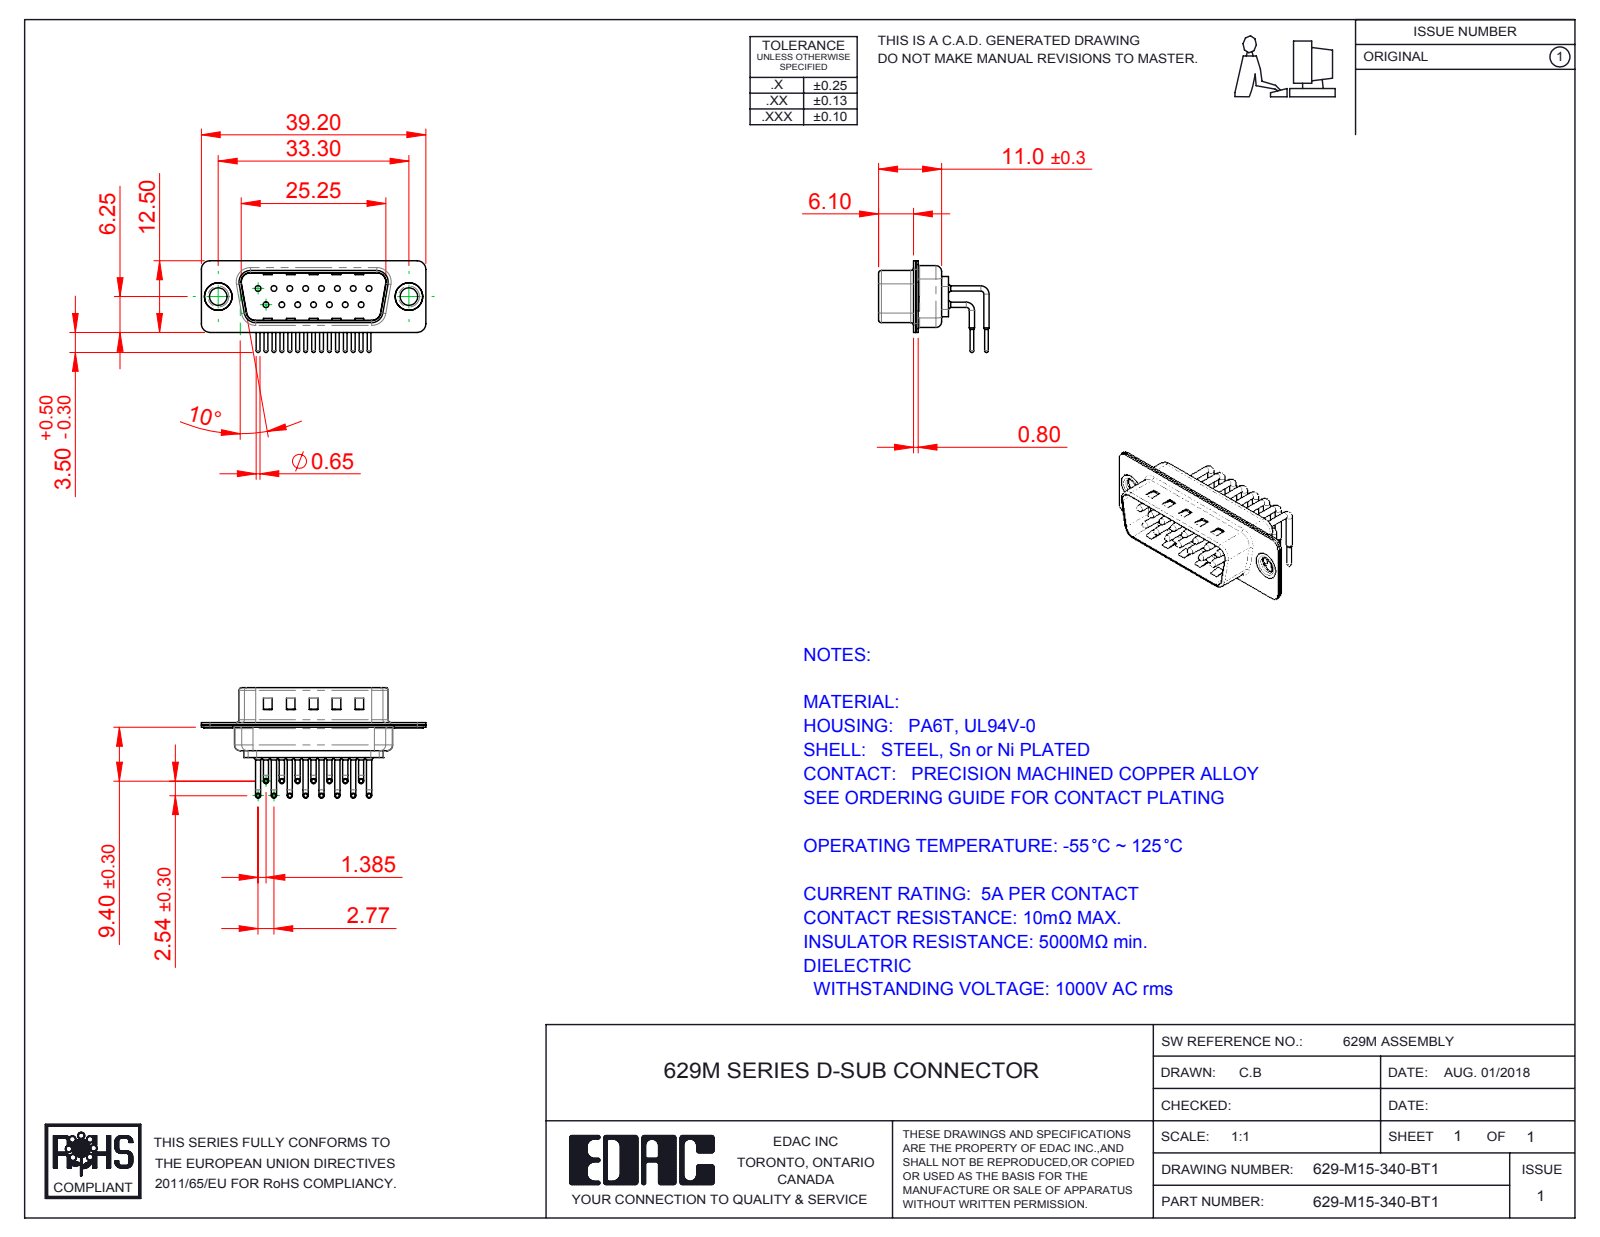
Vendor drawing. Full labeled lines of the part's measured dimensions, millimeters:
Part name (STEP PRODUCT): 629M Thru Hole Rivet; 629M Contact Row 1; 629M Contact Row 2; 629-M15-340-BT1 (+3 more)
STEP written by: SolidWorks 2016 (CONFIG_CONTROL_DESIGN)
Units: millimetres
Bodies: 20 solids, 1964 faces (1099 planar, 657 cylindrical, 208 other)
Overall size (bounding box): 39.2 × 19.29 × 16
Volume: 1 881 mm³ · Surface area: 5 213 mm²
Round holes (diameter × count): ⌀1 ×15, ⌀1.7 ×15, ⌀2 ×15, ⌀3.05 ×2, ⌀4 ×2, ⌀4.8 ×2
Round bosses / shafts (diameter × count): ⌀0.9 ×30, ⌀1.5 ×15, ⌀0.65 ×15, ⌀5 ×2, ⌀4.9 ×2, ⌀3.55 ×2
Partial cylindrical surfaces — rounded edges, fillets, slot ends (radius × count): R1.5 ×16, R1.01 ×15, R2 ×12, R0.5 ×8, R1.6 ×8, R0.25 ×4, R0.6 ×4, R0.65 ×4
Main face-to-face distances: 0.4, 0.85, 9.55, 8.7, 1.25, 0.8, 10.4, 1.5, 0.35, 1.9
Hole centre spacings: 3.16, 2.77, 5.54, 8.31, 11.08, 5.03, 5.04, 7.48
